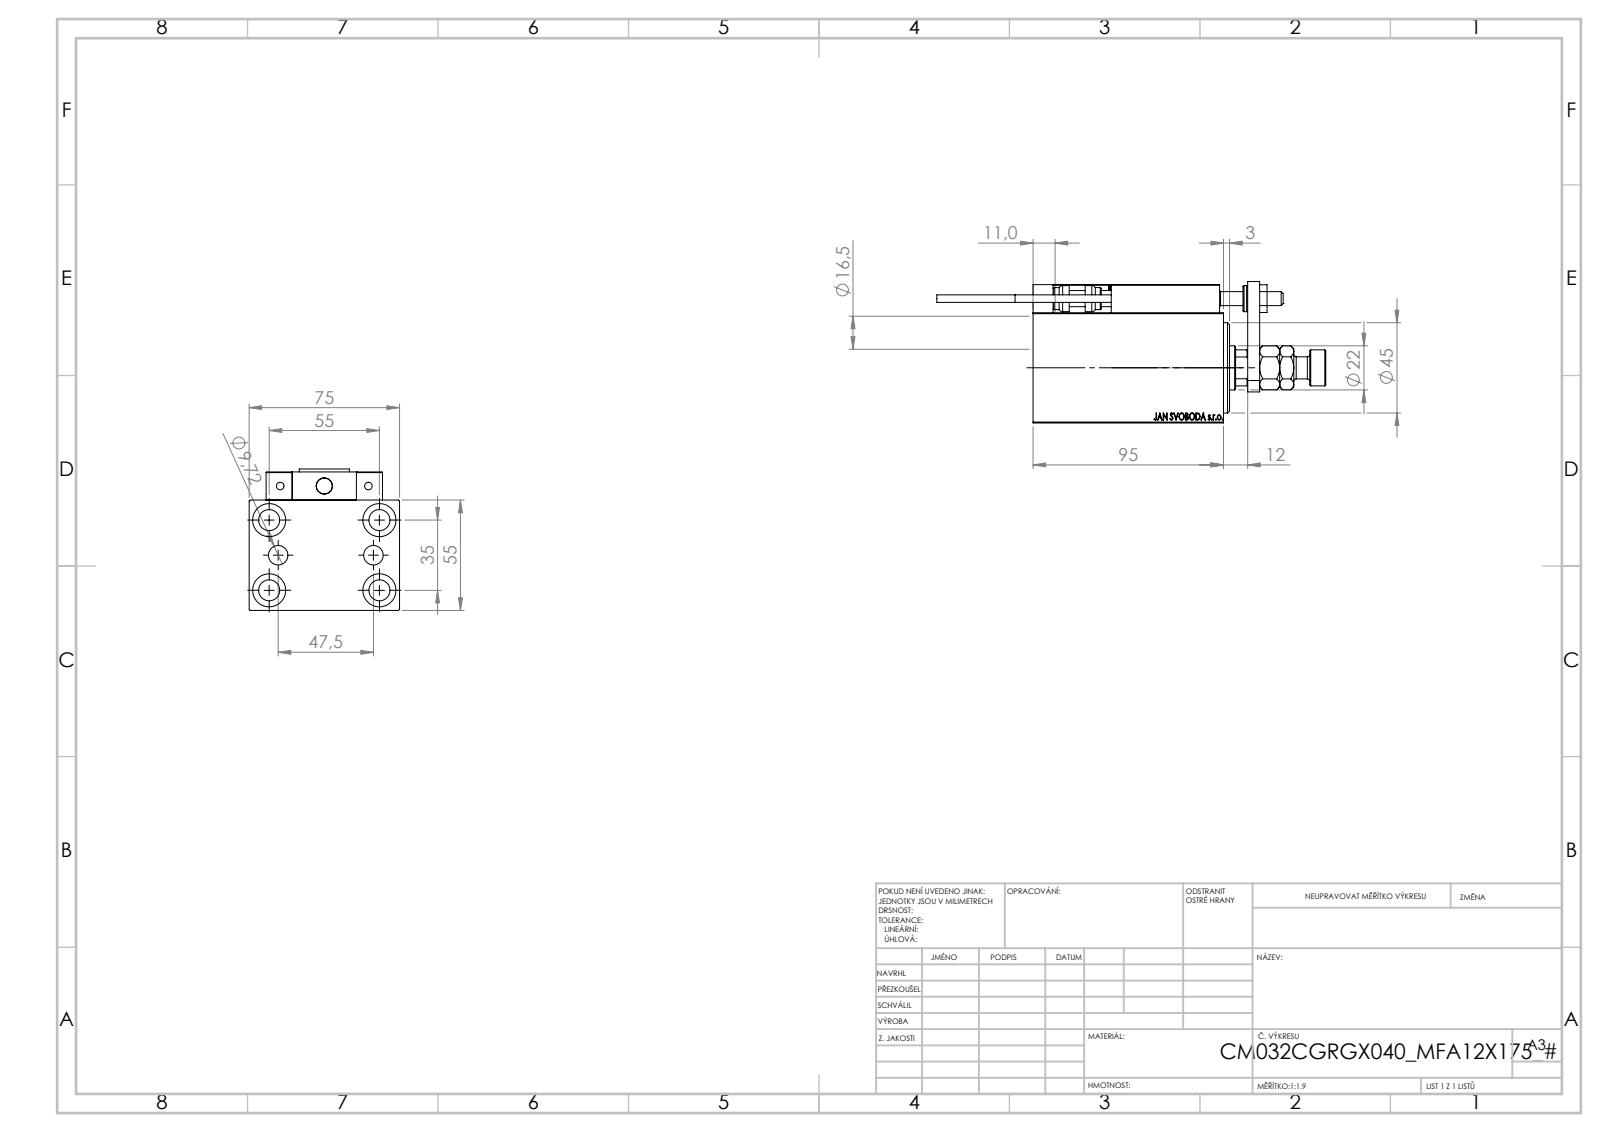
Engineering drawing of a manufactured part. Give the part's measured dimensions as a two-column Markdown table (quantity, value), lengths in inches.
| quantity | value |
| --- | --- |
| part name | Block; ALLEN BOLT D5; SWITCH DIM B,W; V450CM_C_Body (+7 more) |
| STEP written by | SolidWorks 2019 (CONFIG_CONTROL_DESIGN) |
| units | inches |
| bodies | 24 solids, 1330 faces (576 planar, 188 cylindrical, 566 other) |
| overall size | 7.638 × 2.953 × 2.776 |
| volume | 23.78 in³ |
| surface area | 148.3 in² |
| round holes (diameter × count) | 0.157 × 6, 0.315 × 5, 0.413 × 5, 0.65 × 5, 0.126 × 4, 0.197 × 2, 0.383 × 2, 0.276 × 1, 0.866 × 1, 1.004 × 1, 1.26 × 1, 1.339 × 1 |
| round bosses / shafts (diameter × count) | 0.433 × 2, 0.197 × 2, 0.15 × 2, 0.709 × 1, 0.512 × 1 |
| partial cylindrical surfaces (radius × count) | 0.012 × 30, 0.118 × 2, 0.413 × 1 |
| main face-to-face distances | 2.165, 2.953, 0.551, 0.197, 1.772, 0.118, 2.717, 0.236, 0.906, 0.709 |
| hole center spacings | 0.705, 1.283, 2.132, 0.448, 0.787, 0.935, 1.165, 1.169 |
